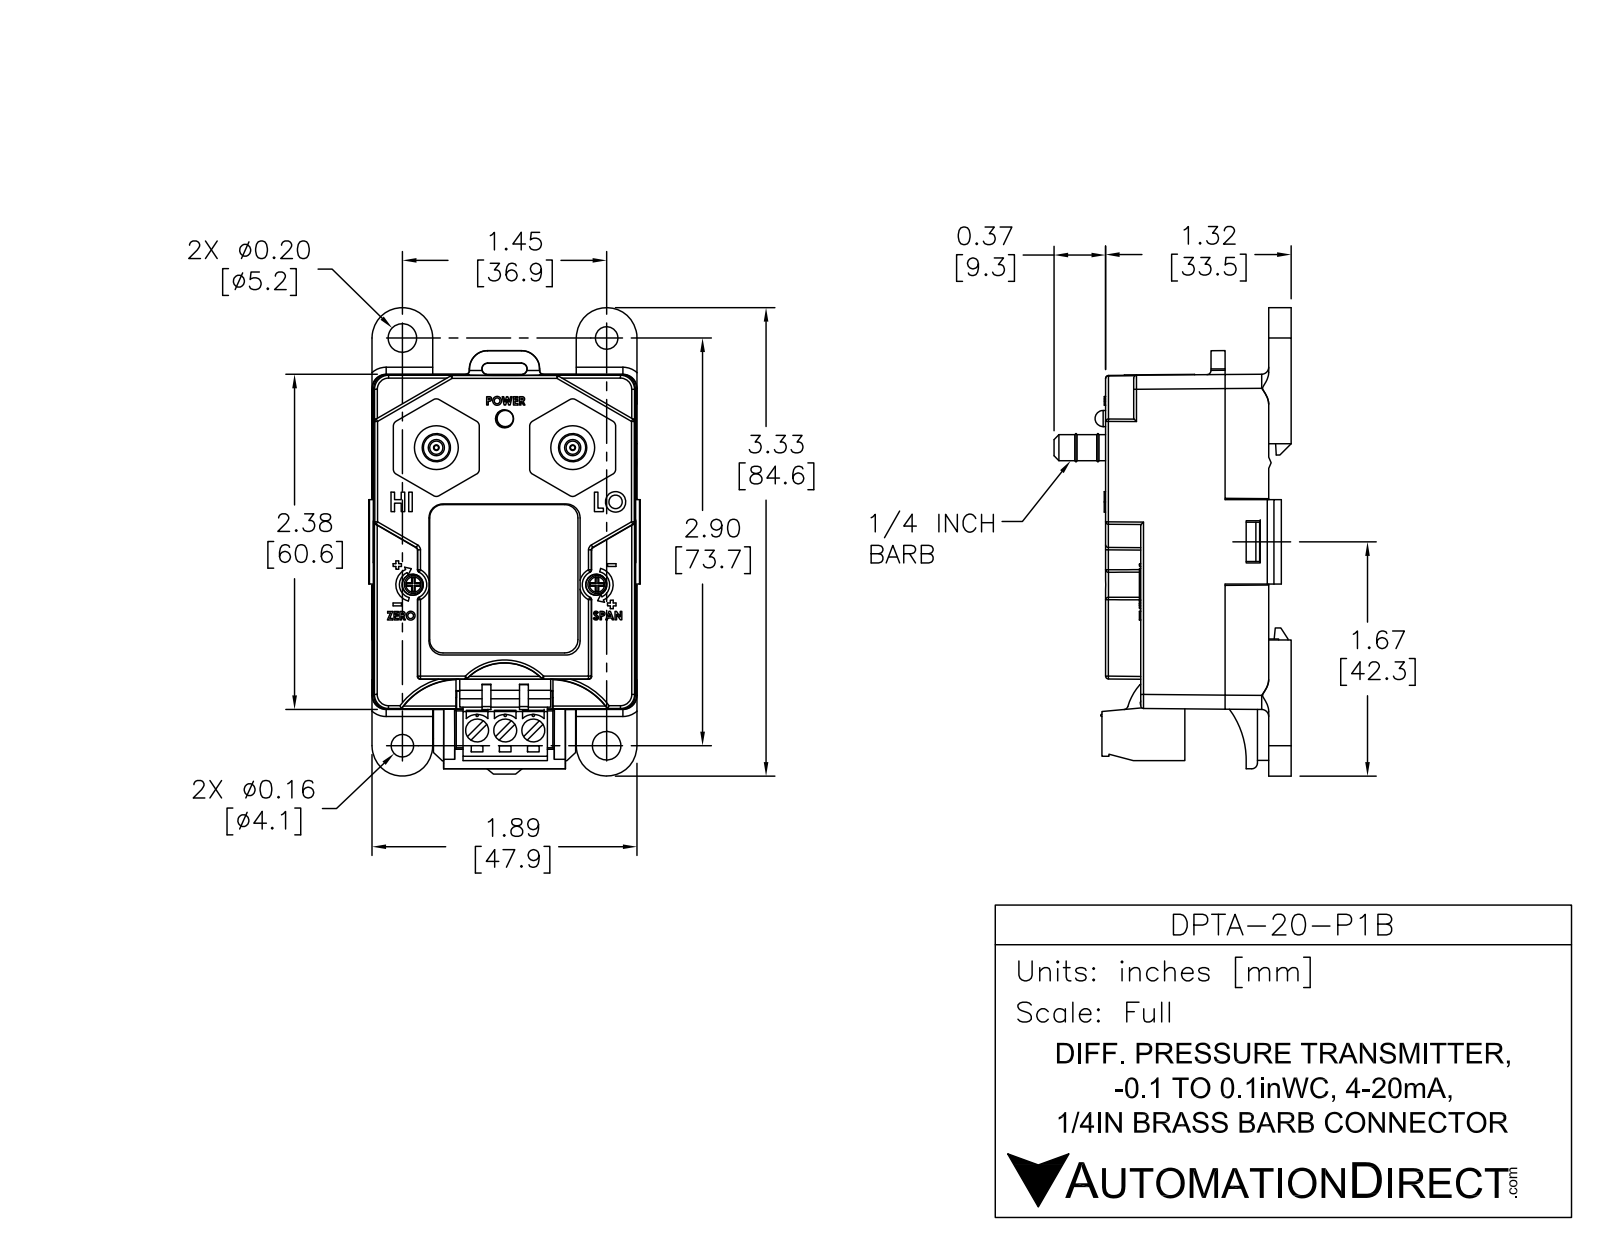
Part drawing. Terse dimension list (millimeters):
name: DPTA-20-P1B
written by: SolidWorks 2013 (AUTOMOTIVE_DESIGN)
unit: mm
bodies: 11 solids, 506 faces (354 planar, 134 cylindrical, 18 other)
size: 85.01 × 49.76 × 43.1
volume: 29 684 mm³; area: 34 743 mm²
holes: 7× ⌀4, 2× ⌀2.5, 2× ⌀5.12, 1× ⌀3.1
bosses: 3× ⌀5, 3× ⌀3.5, 3× ⌀3.5, 2× ⌀8, 2× ⌀4.75, 1× ⌀3
rounds: 12× R3, 4× R2, 4× R5.5, 2× R0.99, 2× R1.06, 2× R1.12, 2× R2.38, 2× R3.25
face distances: 1, 1.9, 4, 29.1, 0.5, 46.9, 5.9, 5, 33.1, 27.2
hole spacings: 13.55, 20.73, 23.37, 24.92, 29.43, 34.46, 36.67, 38.22
